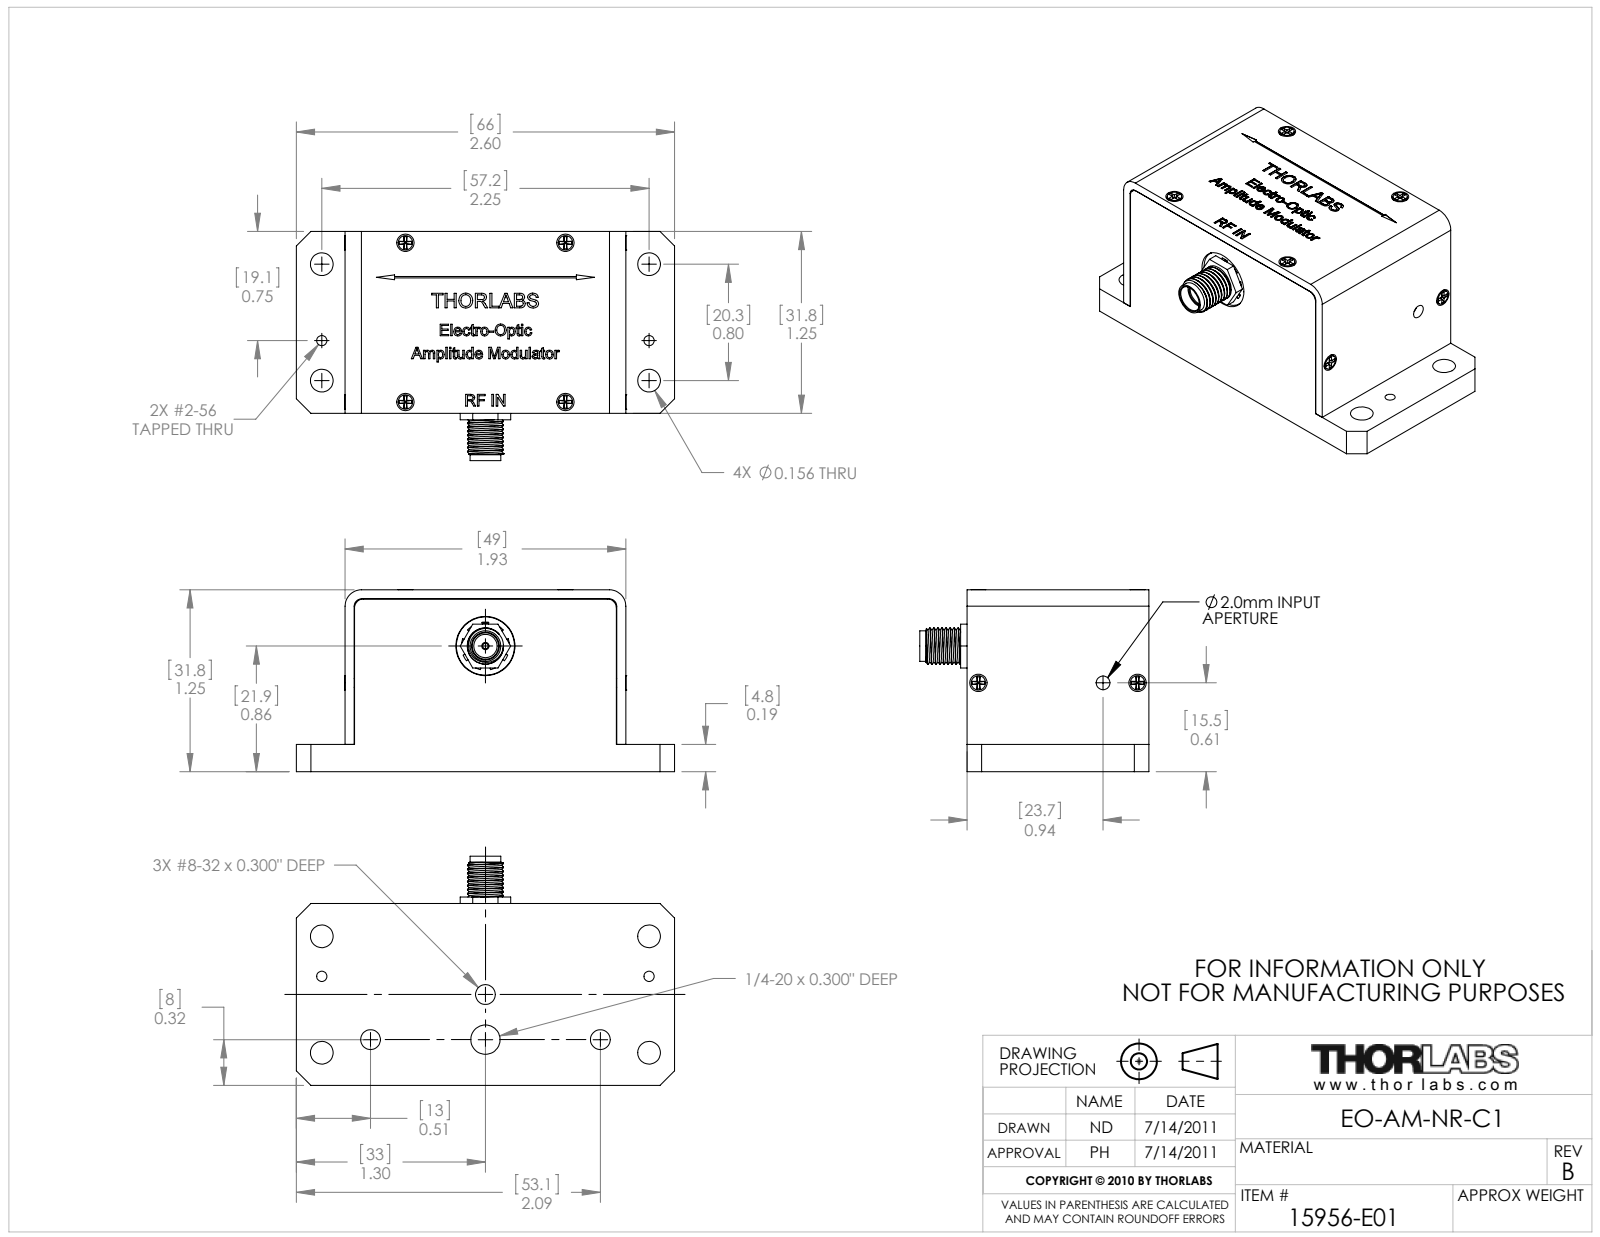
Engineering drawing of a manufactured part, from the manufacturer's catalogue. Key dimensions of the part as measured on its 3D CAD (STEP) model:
Part name (STEP PRODUCT): 15956-E01
STEP written by: SolidWorks 2011 (AUTOMOTIVE_DESIGN)
Units: millimetres
Bodies: 13 solids, 1048 faces (588 planar, 172 cylindrical, 288 other)
Overall size (bounding box): 66.04 × 40.01 × 31.79
Volume: 28 212 mm³ · Surface area: 18 817 mm²
Round holes (diameter × count): ⌀1.78 ×8, ⌀1.19 ×6, ⌀3.96 ×4, ⌀3.45 ×3, ⌀0.94 ×1, ⌀1.27 ×1, ⌀2.38 ×1, ⌀4.06 ×1, ⌀4.19 ×1, ⌀4.6 ×1, ⌀5.11 ×1, ⌀6.35 ×1
Round bosses / shafts (diameter × count): ⌀2.51 ×6, ⌀1.52 ×6, ⌀10.16 ×1, ⌀8 ×1, ⌀6.3 ×1, ⌀5.33 ×1, ⌀1.27 ×1
Partial cylindrical surfaces — rounded edges, fillets, slot ends (radius × count): R1.59 ×5, R1.27 ×2, R2.86 ×2, R3.26 ×2, R3.49 ×1, R4.19 ×1
Main face-to-face distances: 31.76, 3.18, 28.58, 30.18, 1.59, 47.43, 25.4, 1.58, 8.89, 21.29
Hole centre spacings: 15.08, 19.7, 28.14, 30.33, 42.71, 48.88, 27.78, 57.16
